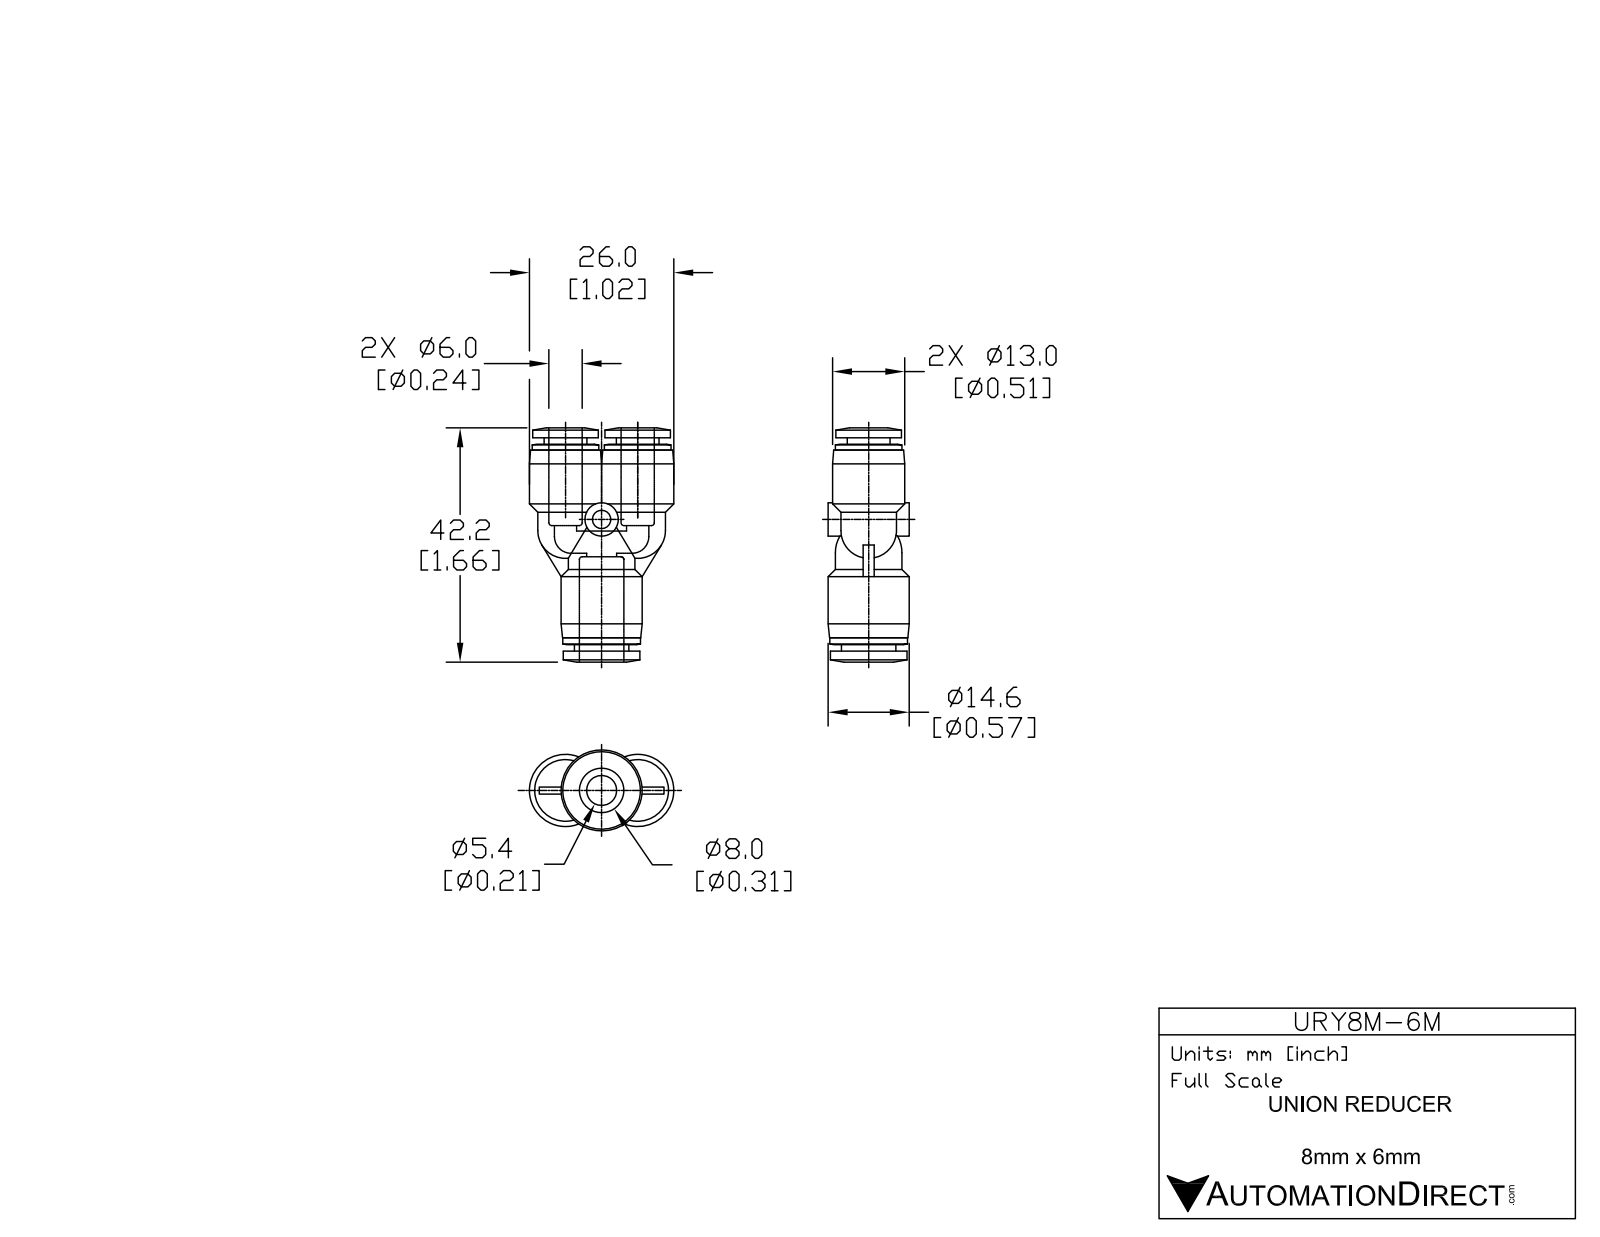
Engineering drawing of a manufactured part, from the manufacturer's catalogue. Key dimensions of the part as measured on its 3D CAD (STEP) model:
Part name (STEP PRODUCT): URY8M-6M
STEP written by: SolidWorks 2015 (AUTOMOTIVE_DESIGN)
Units: inches
Bodies: 1 solid, 108 faces (21 planar, 44 cylindrical, 43 other)
Overall size (bounding box): 1.642 × 1.024 × 0.575
Volume: 0.342 in³ · Surface area: 7.53 in²
Round holes (diameter × count): ⌀0.248 ×2, ⌀0.13 ×1, ⌀0.327 ×1
Round bosses / shafts (diameter × count): ⌀0.472 ×3, ⌀0.512 ×2, ⌀0.465 ×2, ⌀0.303 ×2, ⌀0.575 ×1, ⌀0.551 ×1, ⌀0.543 ×1, ⌀0.386 ×1
Partial cylindrical surfaces — rounded edges, fillets, slot ends (radius × count): R0.197 ×2
Main face-to-face distances: 0.045, 1.447, 1.492, 1.402, 0.654, 0.608, 0.793, 0.839, 0.248, 0.327
Hole centre spacings: 0.256, 0.512
